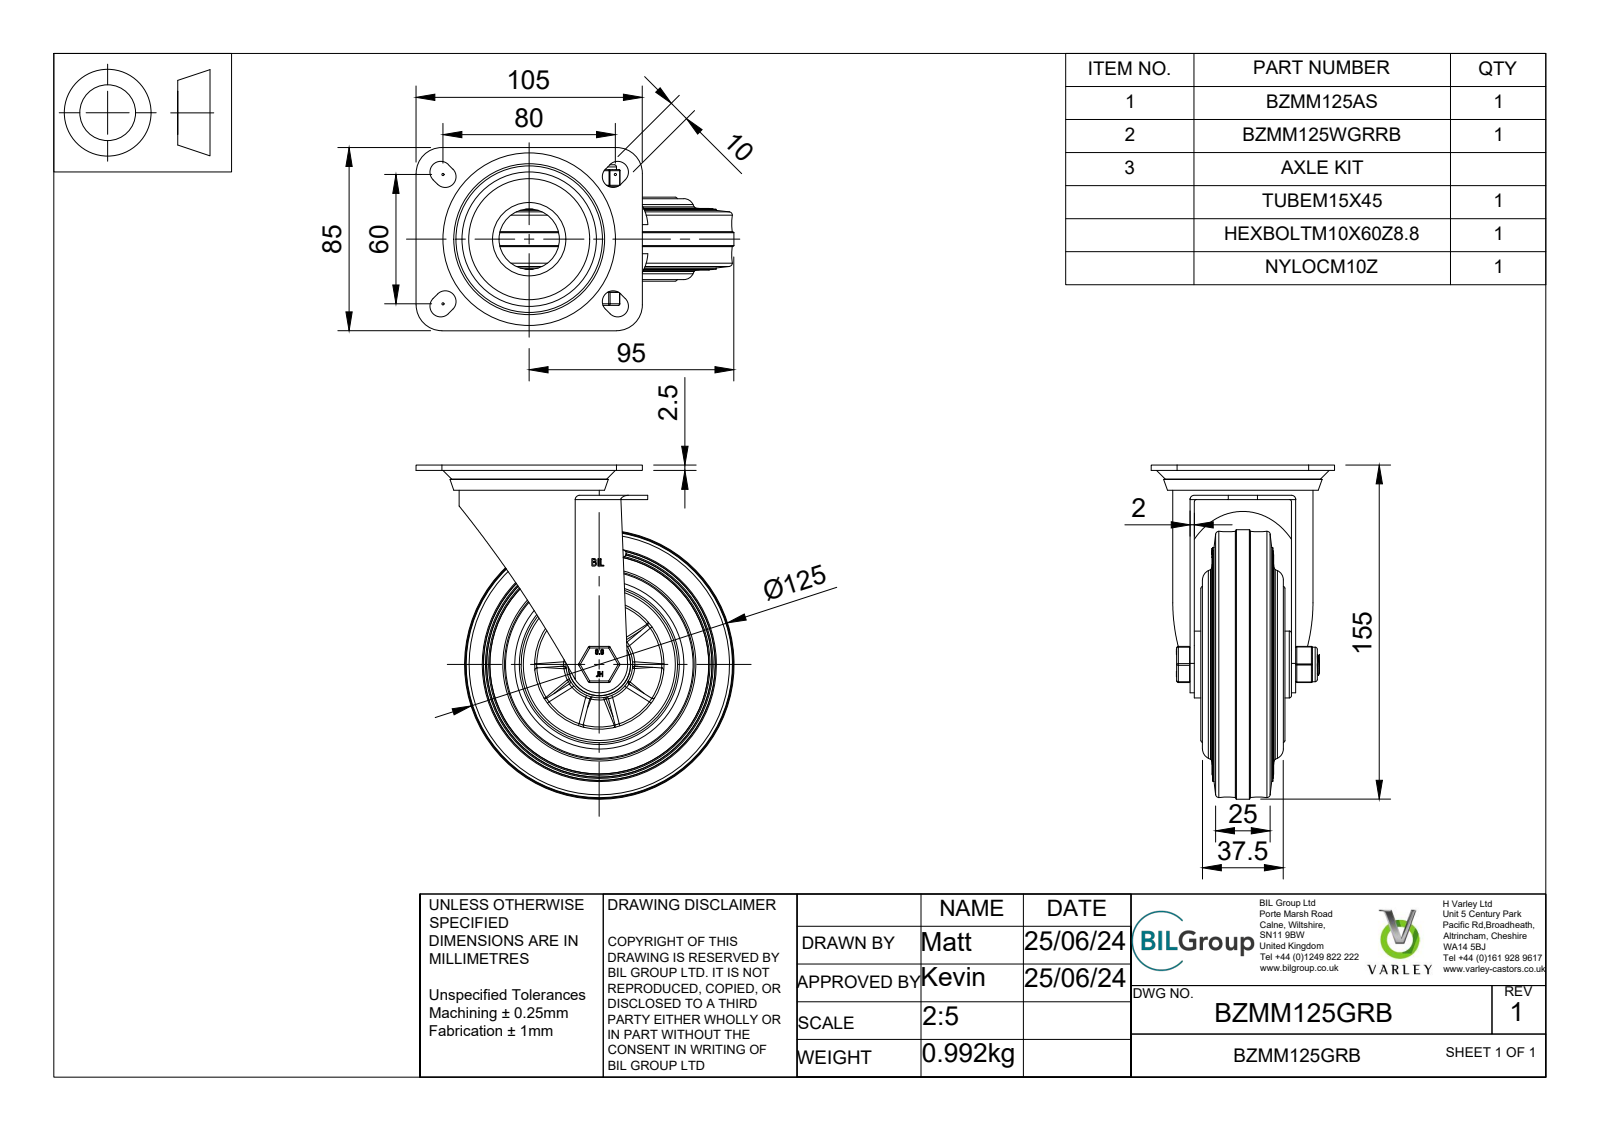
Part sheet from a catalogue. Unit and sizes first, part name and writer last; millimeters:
Units: millimetres
Overall size (bounding box): 155 × 147.5 × 85
Round holes (diameter × count): ⌀10 ×1, ⌀10.2 ×1, ⌀10.3 ×1, ⌀12 ×1, ⌀15 ×1, ⌀15.2 ×1, ⌀22.75 ×1, ⌀28 ×1, ⌀29 ×1, ⌀60 ×1, ⌀61 ×1, ⌀67.5 ×1
Round bosses / shafts (diameter × count): ⌀4 ×8, ⌀125 ×1, ⌀65 ×1, ⌀49 ×1, ⌀34 ×1, ⌀31 ×1, ⌀28.9 ×1, ⌀16 ×1
Partial cylindrical surfaces — rounded edges, fillets, slot ends (radius × count): R0.5 ×18, R0.75 ×12, R5 ×8, R1 ×4, R12 ×4, R2 ×2, R20.69 ×2, R9.38 ×1
Main face-to-face distances: 2, 5, 2.5, 9.5, 4.5, 11.5, 7.5, 47, 7, 6.5
Volume: 394 821 mm³ · Surface area: 145 283 mm²
Bodies: 19 solids, 766 faces (221 planar, 156 cylindrical, 389 other)
Part name (STEP PRODUCT): BZMM125GRB v4; BZMM125AS - 2 v2; ZINC PLATED, PRESSED STEEL TOP PLATE; ZINC PLATED, PRESSED STEEL FORKS (+8 more)
STEP written by: Autodesk Translation Framework v13.14.0.145 (AUTOMOTIVE_DESIGN)
